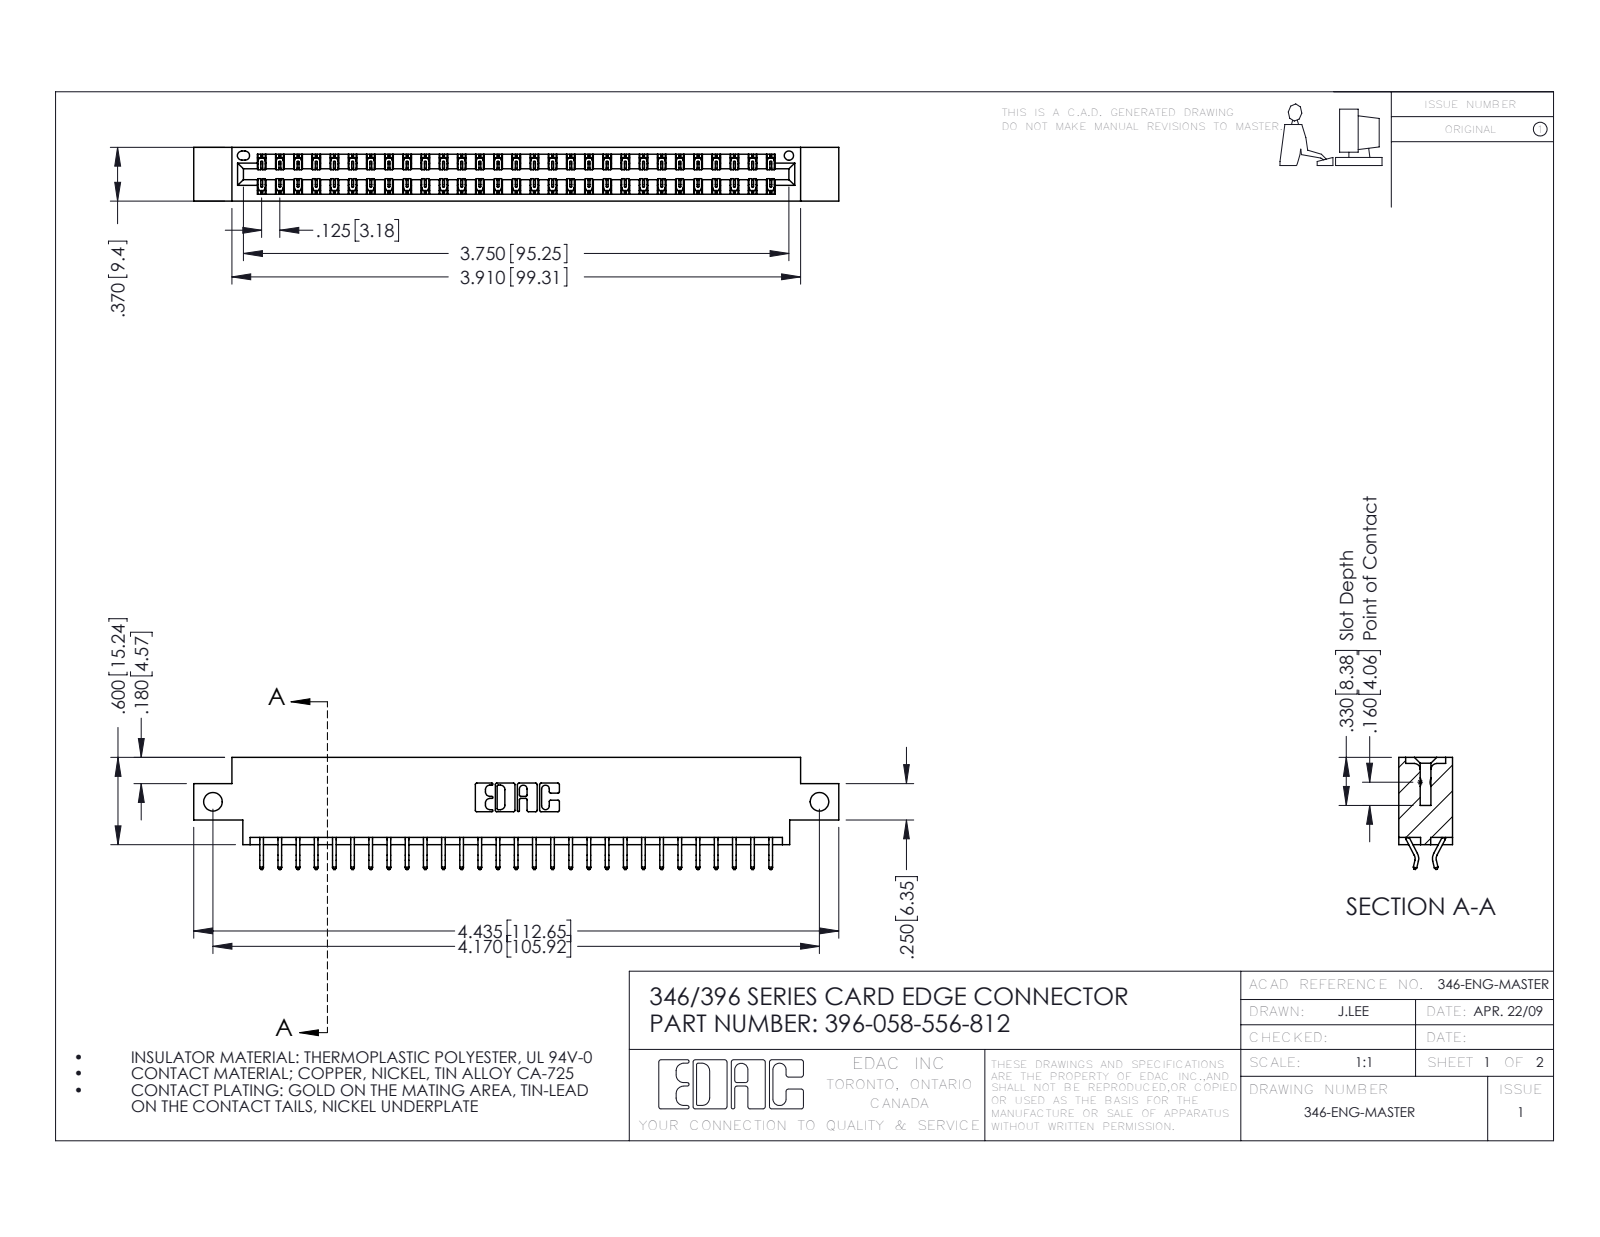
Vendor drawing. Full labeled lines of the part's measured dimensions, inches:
Part name (STEP PRODUCT): 396-058-556-812; 346 Part_0.170 Offset - Side Mount; 345-292-001_556 Tail
STEP written by: SolidWorks 2016 (CONFIG_CONTROL_DESIGN)
Units: inches
Bodies: 59 solids, 3490 faces (2342 planar, 1148 cylindrical, 0 other)
Overall size (bounding box): 4.435 × 0.77 × 0.37
Volume: 0.649 in³ · Surface area: 22.33 in²
Round holes (diameter × count): ⌀0.128 ×2, ⌀0.064 ×1
Partial cylindrical surfaces — rounded edges, fillets, slot ends (radius × count): R0.006 ×87, R0.01 ×22, R0.007 ×6, R0.031 ×6, R0.026 ×3, R0.01 ×2, R0.014 ×2, R0.022 ×2
Main face-to-face distances: 0.048, 0.322, 0.37, 0.25, 0.025, 0.072, 0.298, 0.275, 0.148, 0.222
Hole centre spacings: 4.17
